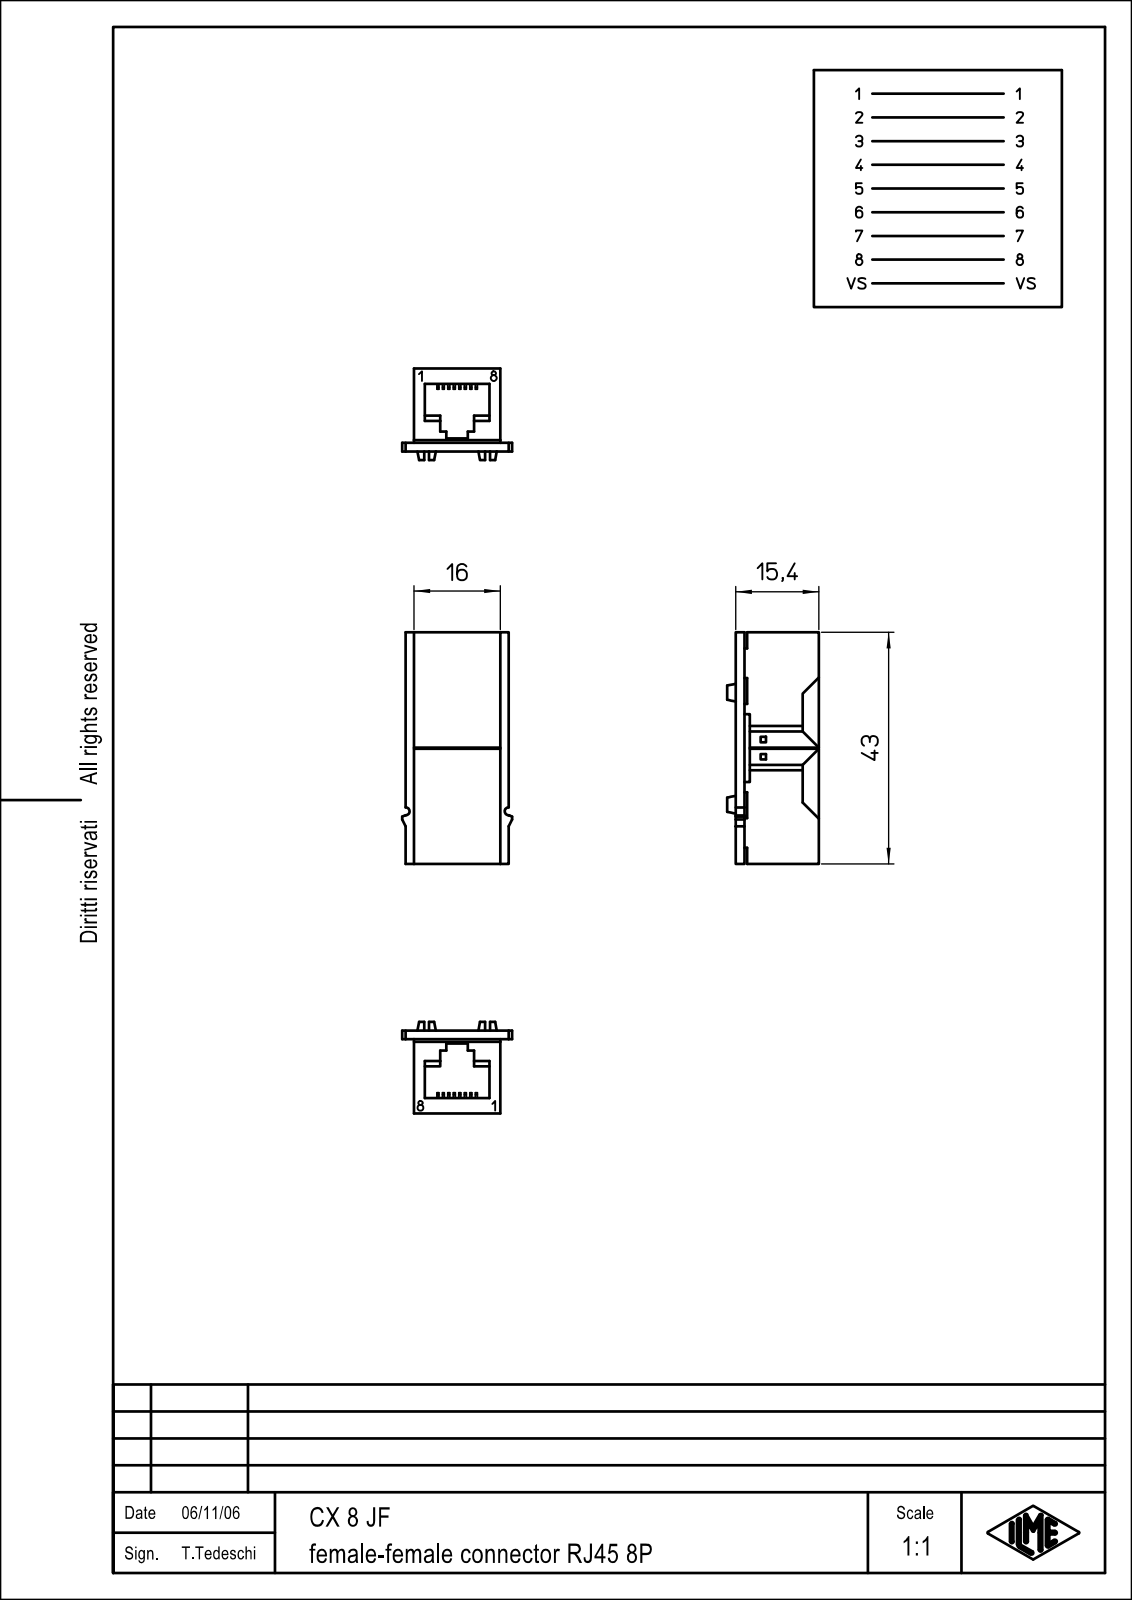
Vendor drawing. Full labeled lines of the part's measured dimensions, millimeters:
Part name (STEP PRODUCT): CX_8_JF
STEP written by: CoCreate Modeling 16.00A 16-Aug-2008 (C) Parametric Technology GmbH (AUTOMOTIVE_DESIGN)
Units: millimetres
Bodies: 1 solid, 116 faces (90 planar, 18 cylindrical, 8 other)
Overall size (bounding box): 43.5 × 20.4 × 17.1
Volume: 8 160 mm³ · Surface area: 6 019 mm²
Round holes (diameter × count): ⌀3.5 ×4
Round bosses / shafts (diameter × count): ⌀3.4 ×4
Partial cylindrical surfaces — rounded edges, fillets, slot ends (radius × count): R0.75 ×2
Main face-to-face distances: 15.4, 1.6, 13.8, 16, 0.5, 2.85, 2, 14, 2.1, 21.4
Hole centre spacings: 11.3, 21.3, 24.11
